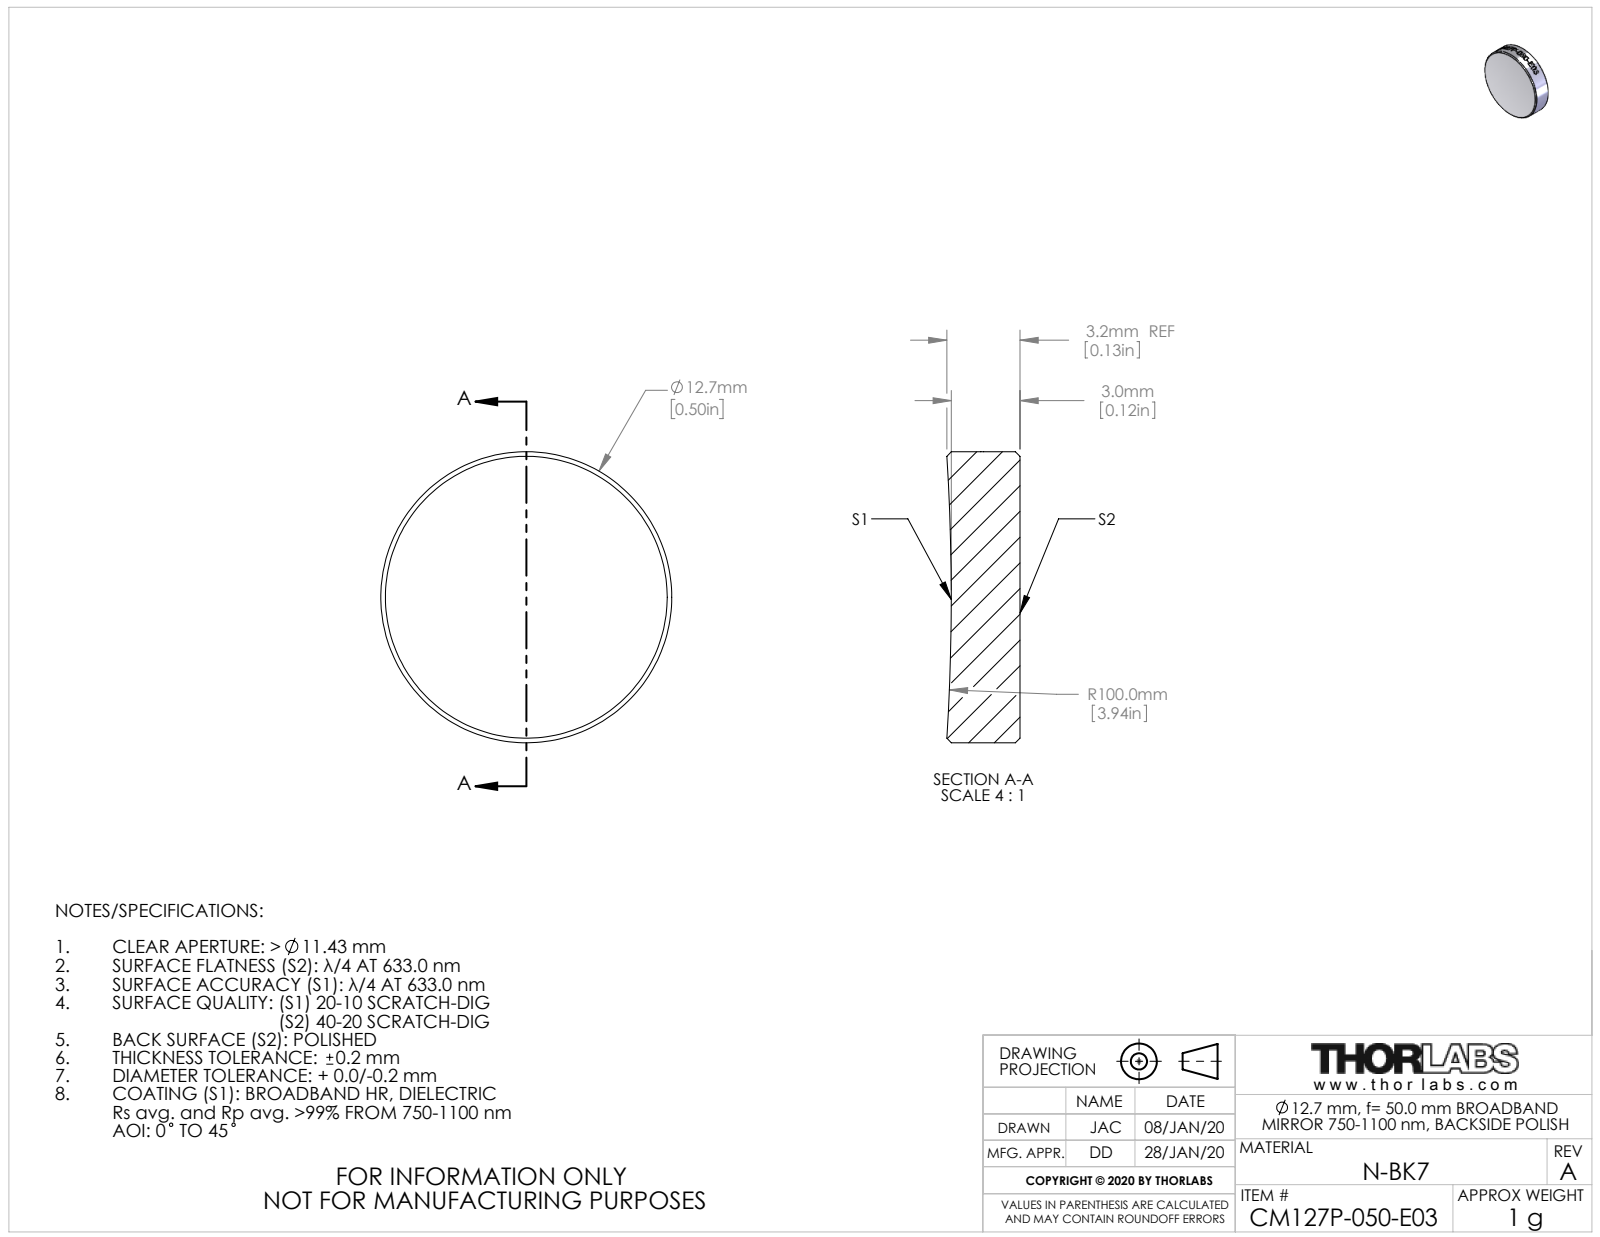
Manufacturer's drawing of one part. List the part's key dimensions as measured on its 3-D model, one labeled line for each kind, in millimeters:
Part name (STEP PRODUCT): TTN201384-E0W
STEP written by: SolidWorks 2018 (CONFIG_CONTROL_DESIGN)
Units: millimetres
Bodies: 1 solid, 27 faces (1 planar, 20 cylindrical, 6 other)
Overall size (bounding box): 12.7 × 12.7 × 3.19
Volume: 391 mm³ · Surface area: 371 mm²
Round bosses / shafts (diameter × count): ⌀12.7 ×1
